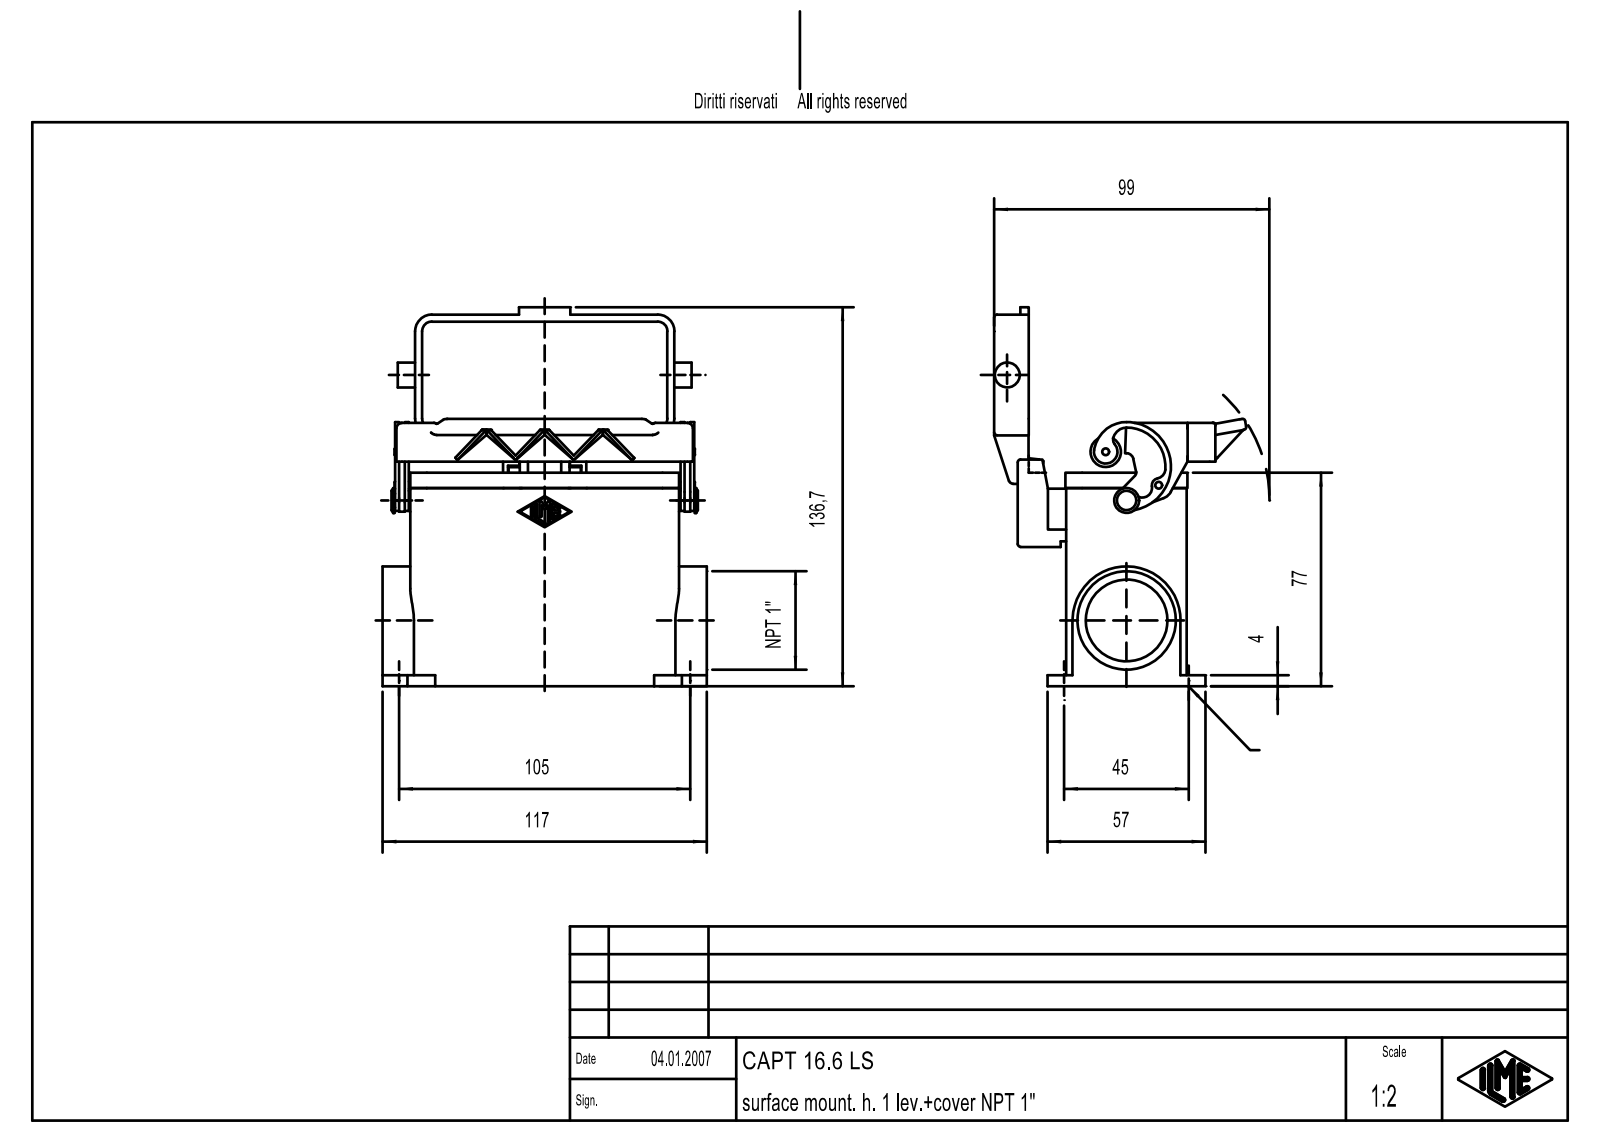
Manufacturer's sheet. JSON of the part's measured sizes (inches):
{"part_name": "p1; p2; p3; p4 (+3 more)", "step_written_by": "Creo Elements/Direct Modeling 18.0B 02-Dec-2011 (C) Parametric Technology GmbH (AUTOMOTIVE_DESIGN)", "units": "inches", "bodies": {"solids": 6, "faces": 568, "planar": 307, "cylindrical": 197, "other": 64}, "overall_size": [5.382, 4.606, 3.581], "volume_in3": 9.813, "surface_area_in2": 134.2, "round_holes": [[0.097, 4], [0.118, 4], [0.217, 4], [0.079, 1], [0.157, 1], [1.161, 1], [1.397, 1]], "round_bosses_or_shafts": [[0.354, 2], [0.197, 2], [0.433, 1], [0.276, 1], [0.157, 1], [0.118, 1], [0.098, 1]], "partial_cylinders_radius": [[0.039, 18], [0.015, 14], [0.079, 12], [0.236, 12], [0.059, 6], [0.138, 6], [0.118, 4], [0.02, 3]], "face_to_face_distances": [0.118, 1.594, 1.713, 0.157, 1.476, 1.024, 2.618, 0.886, 2.736, 1.142], "hole_center_spacings": [0.647, 1.517, 3.61, 3.862, 1.063, 1.772, 3.051, 3.231]}
